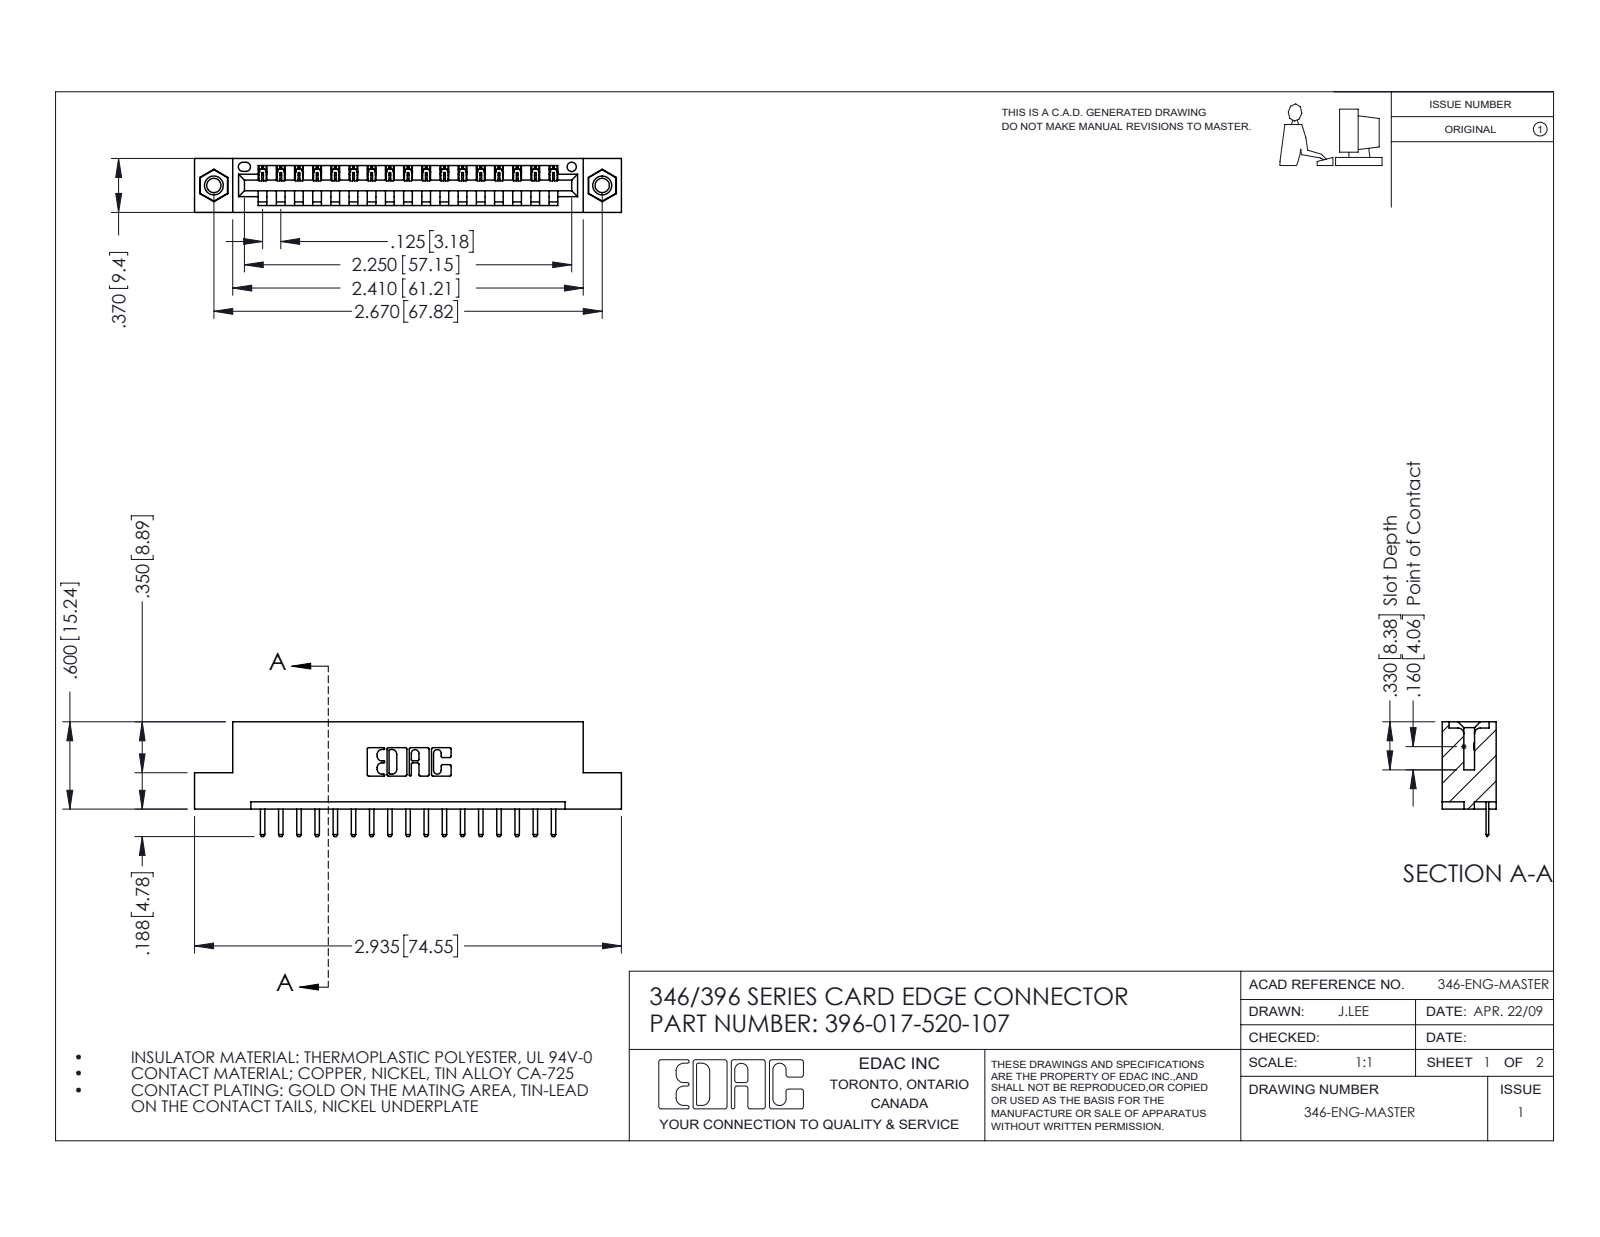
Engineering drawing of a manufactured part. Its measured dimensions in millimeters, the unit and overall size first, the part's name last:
Units: millimetres
Overall size (bounding box): 74.5 × 20 × 9.4
Round holes (diameter × count): ⌀2.5 ×2, ⌀3.2 ×2, ⌀4 ×2, ⌀1.6 ×1
Round bosses / shafts (diameter × count): ⌀3.9 ×2
Partial cylindrical surfaces — rounded edges, fillets, slot ends (radius × count): R0.3 ×36, R0.2 ×34, R0.3 ×22, R0.2 ×6, R0.8 ×6, R0.7 ×3, R0.8 ×2, R1 ×2
Main face-to-face distances: 1.2, 8.2, 9.4, 6.4, 3.8, 5.6, 2.5, 4.4, 1.8, 7.6
Hole centre spacings: 6.2, 62.6, 67.8
Volume: 6 900 mm³ · Surface area: 8 226 mm²
Bodies: 20 solids, 1236 faces (822 planar, 398 cylindrical, 16 other)
Part name (STEP PRODUCT): 345-292-001_345-293-120; 346 Part_Flush Mounting Lugs - 0.156 Dia-TI; 345-250-001_345-250-005-103; 396-017-520-107
STEP written by: SolidWorks 2016 (CONFIG_CONTROL_DESIGN)
